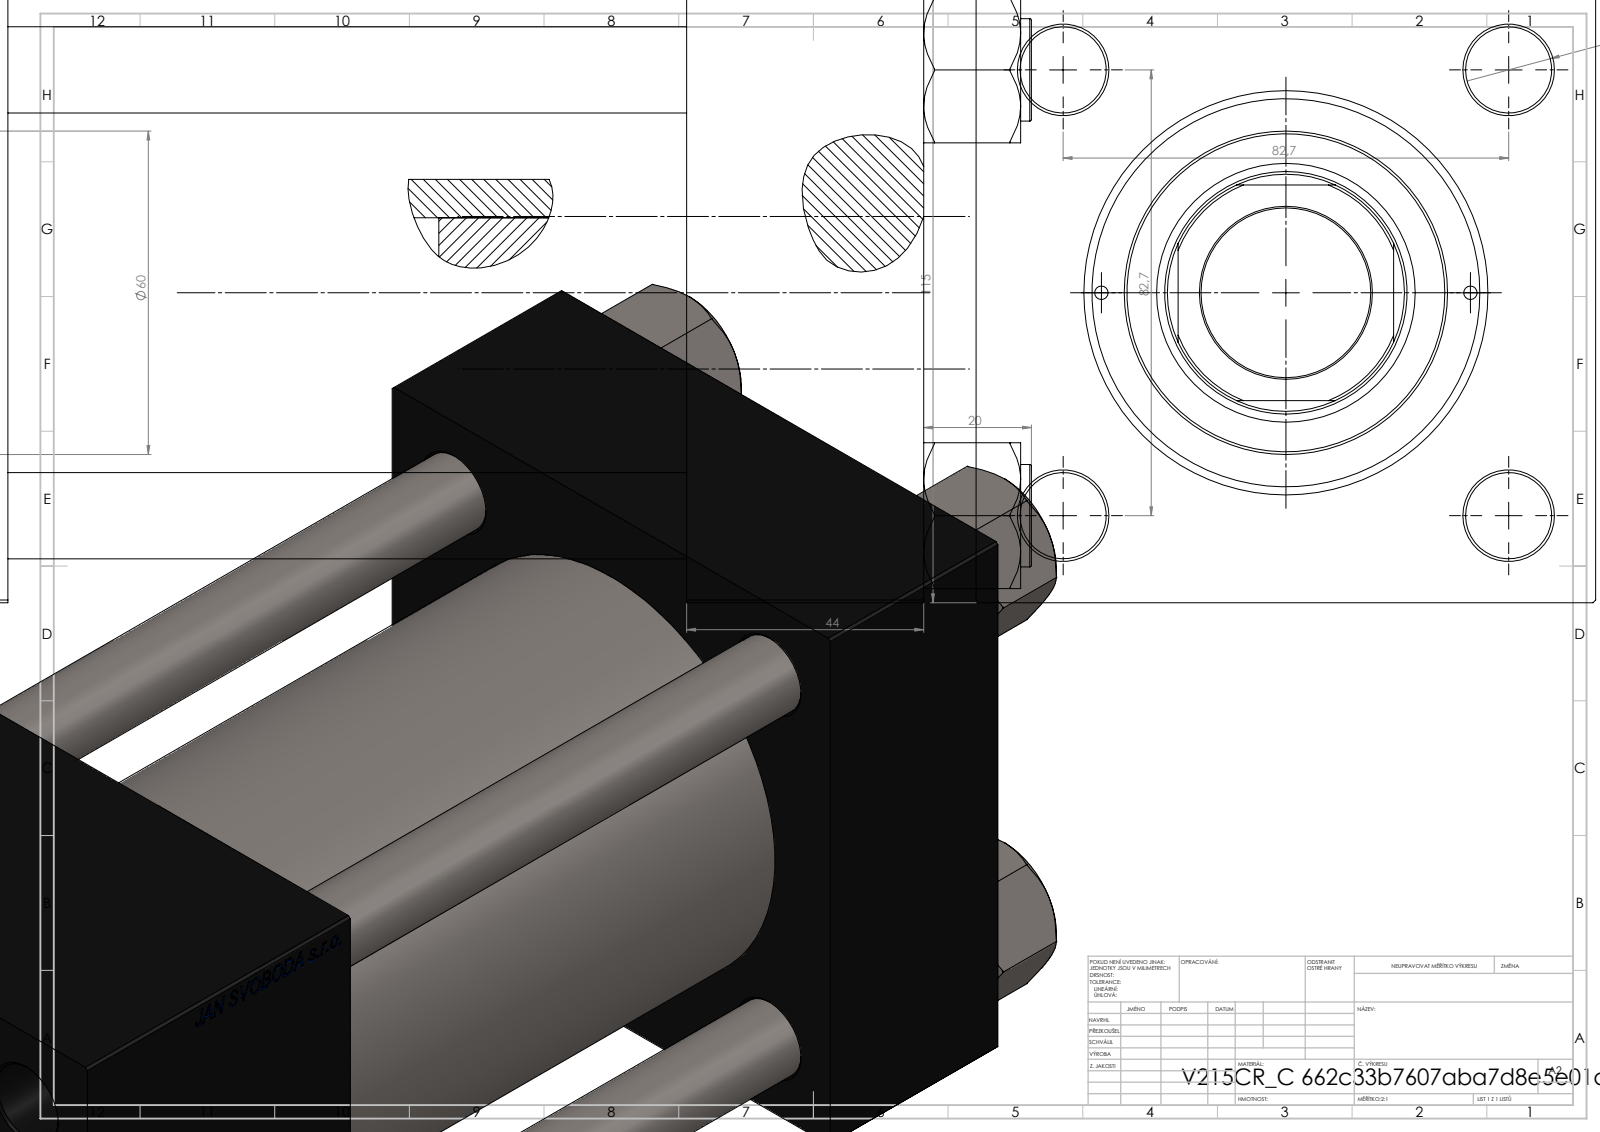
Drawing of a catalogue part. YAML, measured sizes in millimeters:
part_name: "V215CR_C_Body; V215_VC_A; V215CR_C_TYCINKA; NUT_M5_C (+1 more)"
step_written_by: "SolidWorks 2019 (CONFIG_CONTROL_DESIGN)"
units: millimeters
bodies: {solids: 11, faces: 1202, planar: 576, cylindrical: 90, other: 536}
overall_size: [290, 115, 115]
volume: 2010000
surface_area: 325791
round_holes:
  - {diameter: 16, count: 4}
  - {diameter: 2.5, count: 2}
  - {diameter: 7, count: 2}
  - {diameter: 26.44, count: 2}
  - {diameter: 35, count: 2}
  - {diameter: 31.5, count: 1}
  - {diameter: 45, count: 1}
  - {diameter: 48, count: 1}
  - {diameter: 61, count: 1}
  - {diameter: 72, count: 1}
  - {diameter: 80, count: 1}
round_bosses_or_shafts:
  - {diameter: 19, count: 4}
  - {diameter: 86, count: 1}
  - {diameter: 60, count: 1}
partial_cylinders:
  - {radius: 22, count: 1}
face_to_face_distances: [115, 44, 239, 195, 170, 126, 69, 210.3, 166.3, 40.3]
hole_center_spacings: [41.96, 58.48, 82.7, 86.17, 34.25, 116.96, 68.5, 171]
